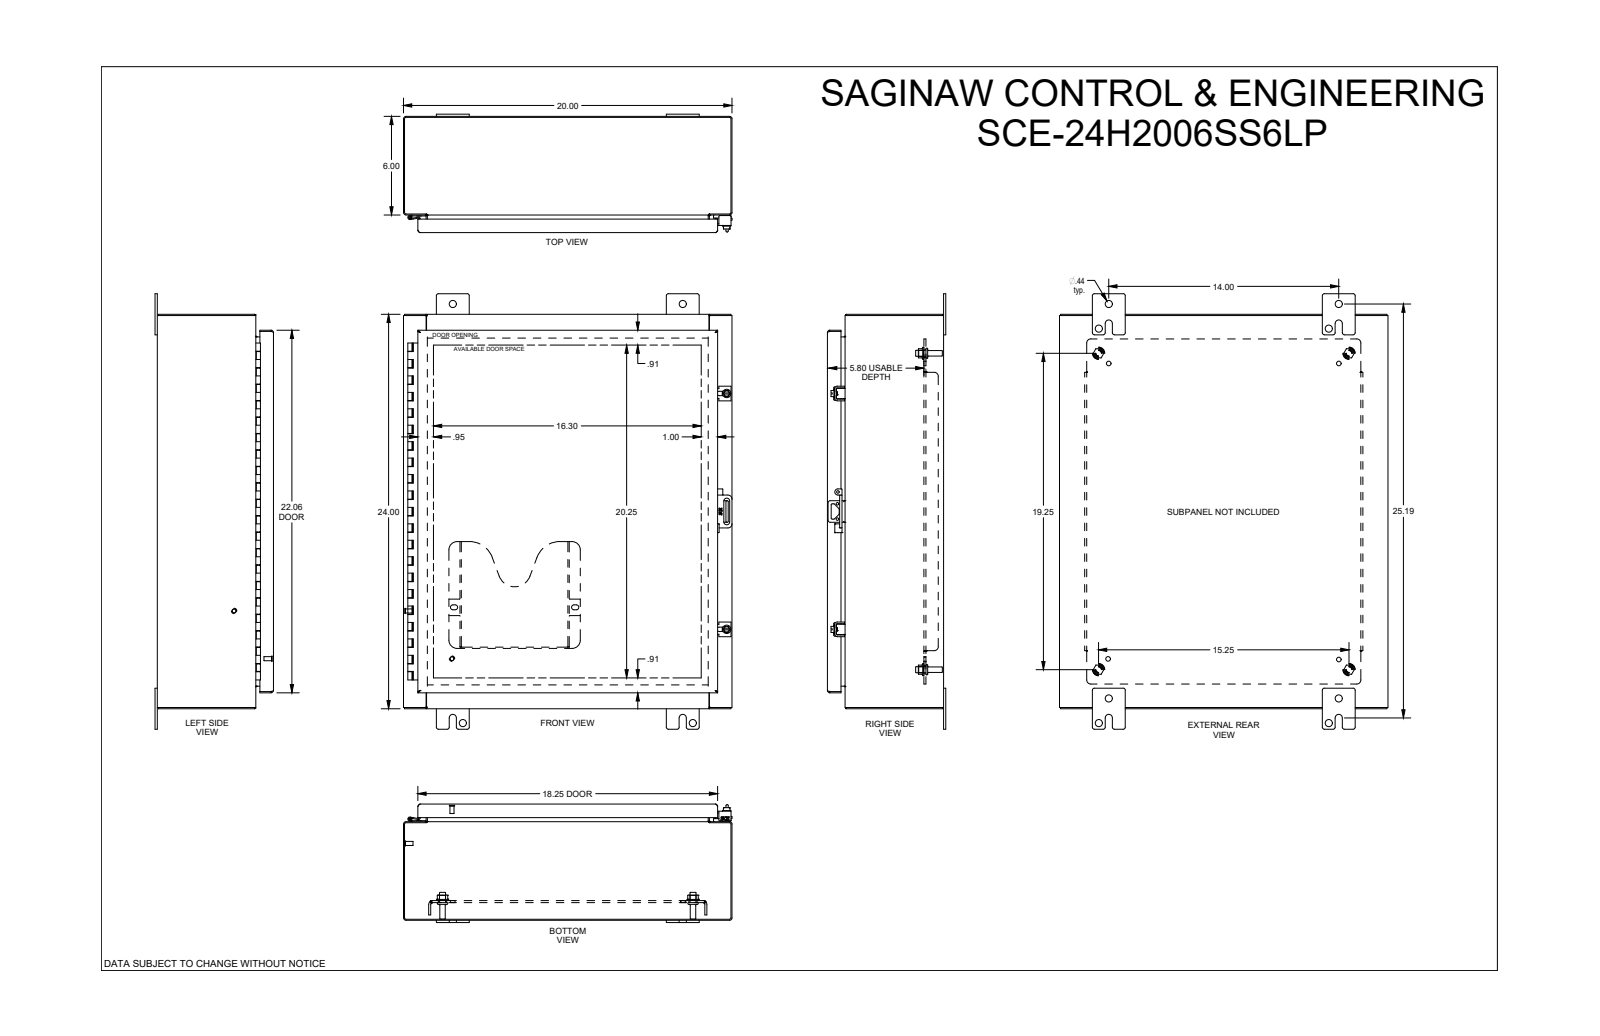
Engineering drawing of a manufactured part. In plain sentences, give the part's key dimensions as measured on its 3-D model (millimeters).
The part is named "SCE-24H2006SS6LP". Its 3-D file was written by "SolidWorks 2019 (CONFIG_CONTROL_DESIGN)". It is 0 solids with 3160 faces: 1275 planar, 660 cylindrical and 1225 other. Overall it measures 673.1 by 508 by 183.1 millimeters. Round holes: 8 of diameter 11.1, 5 of diameter 6.4, 4 of diameter 4.8, 4 of diameter 4.9, 4 of diameter 7.1, 4 of diameter 9.3, 4 of diameter 12.7, 2 of diameter 4.1, 2 of diameter 5.2, 1 of diameter 3.3, 1 of diameter 3.4. Round bosses or shafts: 7 of diameter 6.3, 5 of diameter 14.3, 4 of diameter 9.3, 4 of diameter 8.4, 4 of diameter 6.5, 4 of diameter 4.8, 3 of diameter 6.4, 2 of diameter 12.9. Partial cylindrical surfaces (rounded edges, fillets, slot ends): 114 of radius 0.3, 36 of radius 0.4, 30 of radius 0.7, 27 of radius 0.8, 27 of radius 3.2, 25 of radius 1.5, 22 of radius 1, 14 of radius 1.8. The main face-to-face distances are 1.9, 177.7, 175.8, 1.9, 179.7, 177.7, 150.4, 30.5, 28.6, 147.3. The hole center spacings are 22.2, 355.6, 165.1, 372, 473.5, 601.7, 13.1, 36.6.
